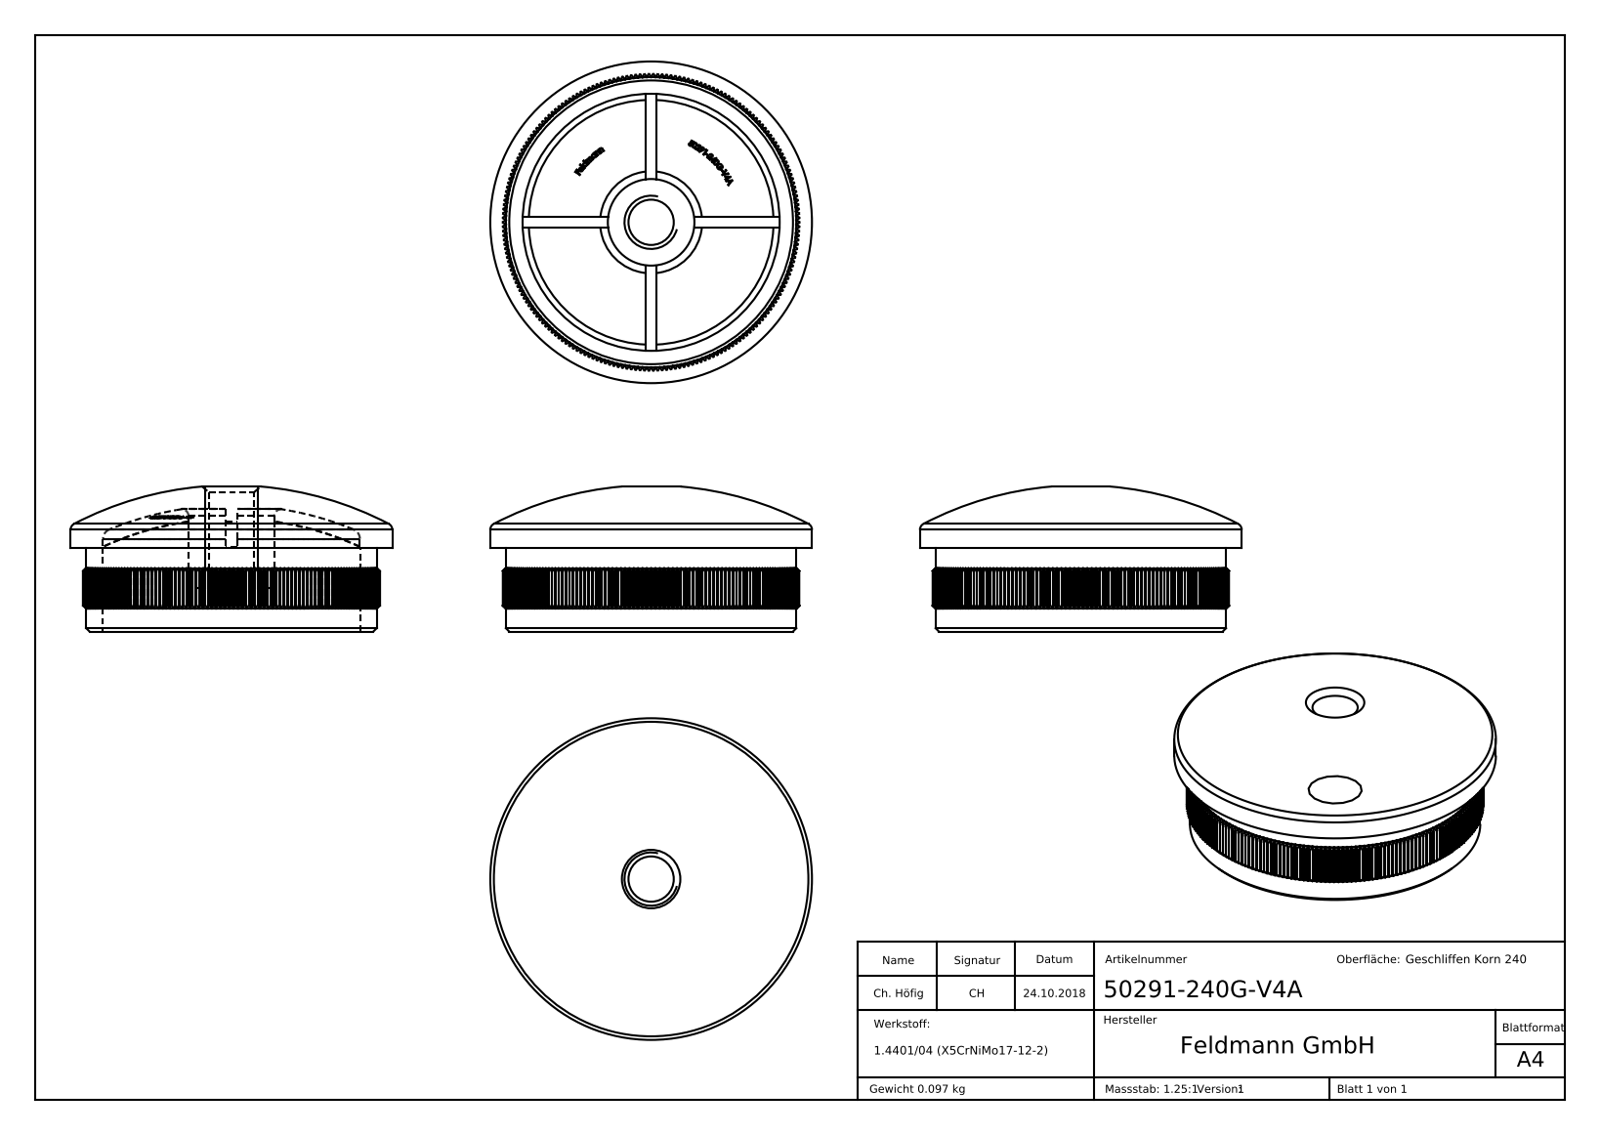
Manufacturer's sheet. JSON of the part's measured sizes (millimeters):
{"part_name": "50291-240G-V4A", "step_written_by": "SolidWorks 2015 (CONFIG_CONTROL_DESIGN)", "units": "millimeters", "bodies": {"solids": 1, "faces": 1789, "planar": 988, "cylindrical": 222, "other": 579}, "overall_size": [48.3, 48.3, 21.78], "volume_mm3": 12161, "surface_area_mm2": 9356, "round_holes": [[6.8, 1], [38.6, 1]], "round_bosses_or_shafts": [[48.3, 1], [43.6, 1], [13, 1]], "partial_cylinders_radius": [[22.25, 1]], "face_to_face_distances": [21.8, 12.5, 21.79, 21.81, 21.78, 21.82, 1.7, 6, 6.5, 3]}
